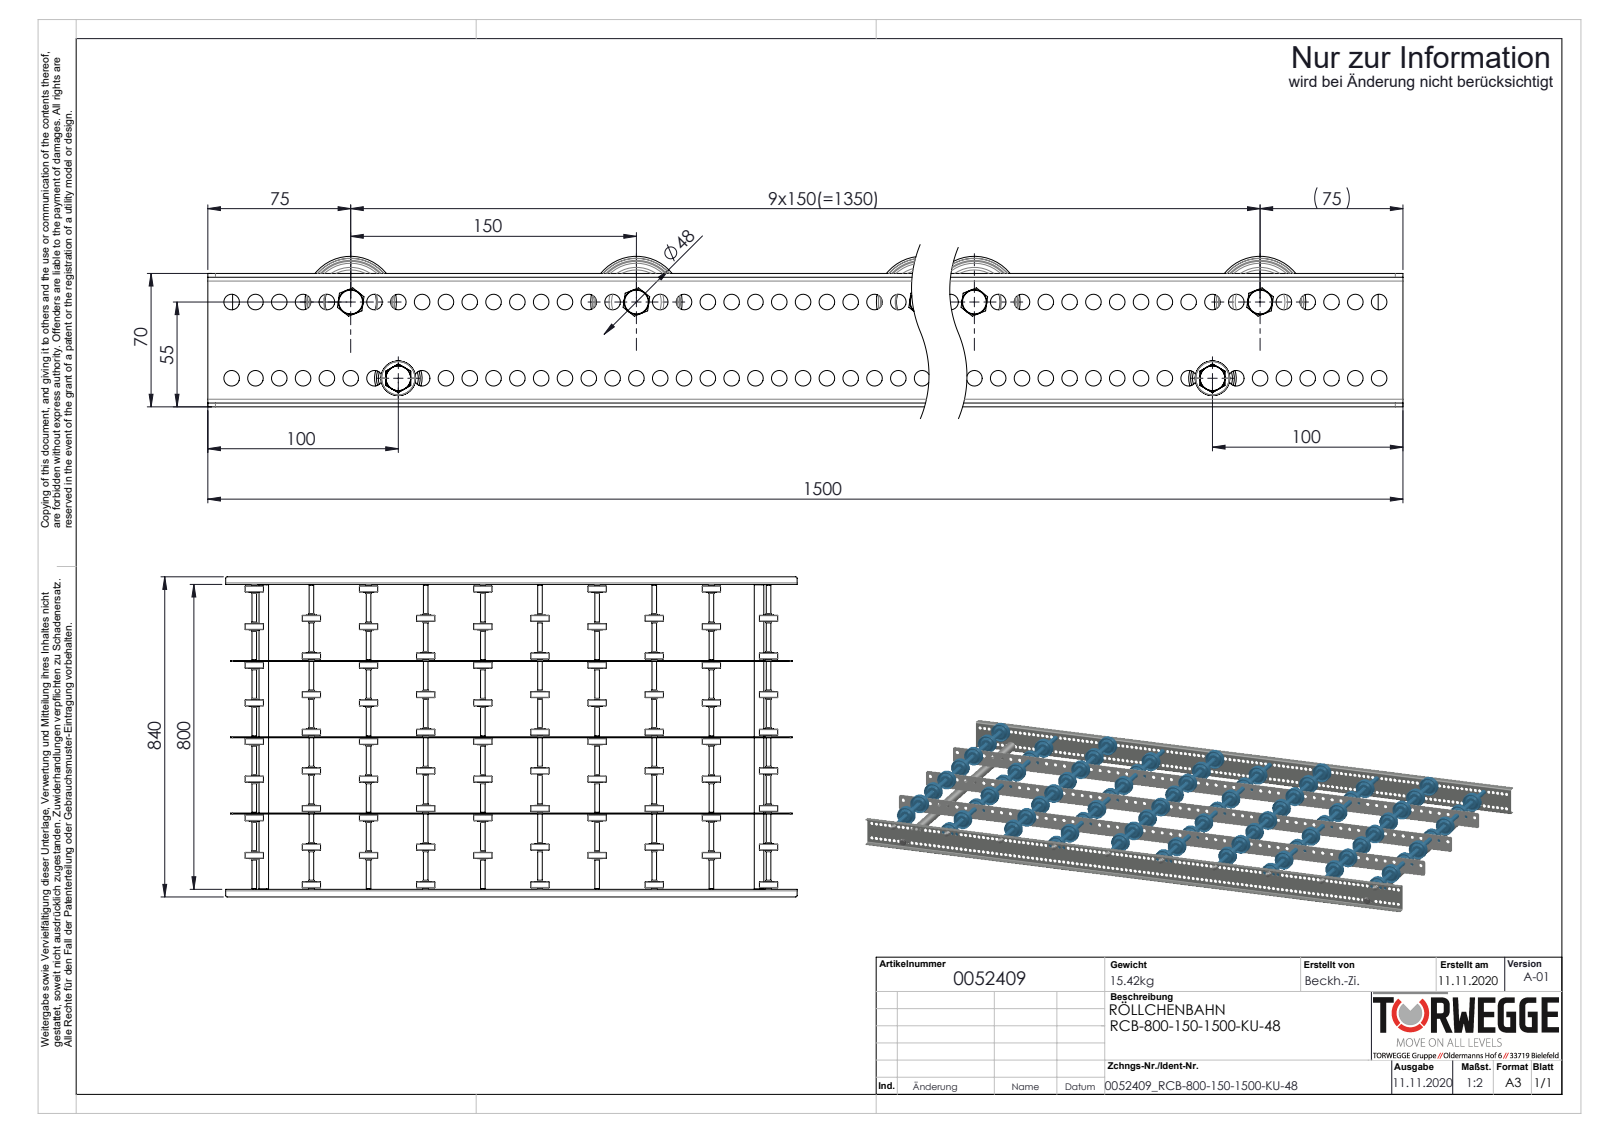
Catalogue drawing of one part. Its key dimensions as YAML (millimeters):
part_name: "0046278_KB-ROHR-12X1,75mm_KFG_L75; Hutmutter_DIN_1587_M8; Röllchenachse-für-Konfiguration_EL800; Traversen_KFG_L800 (+6 more)"
step_written_by: "SolidWorks 2020 (AUTOMOTIVE_DESIGN)"
units: millimeters
bodies: {solids: 205, faces: 8256, planar: 1358, cylindrical: 3234, other: 3664}
overall_size: [1500, 840, 79]
volume: 3458000
surface_area: 2642000
round_holes:
  - {diameter: 8.2, count: 238}
  - {diameter: 8.5, count: 59}
  - {diameter: 6.65, count: 10}
  - {diameter: 9.65, count: 10}
  - {diameter: 13.7, count: 10}
  - {diameter: 6.8, count: 2}
  - {diameter: 21, count: 2}
round_bosses_or_shafts:
  - {diameter: 8, count: 12}
  - {diameter: 48, count: 10}
  - {diameter: 27, count: 10}
  - {diameter: 12.7, count: 10}
  - {diameter: 12.5, count: 10}
  - {diameter: 12, count: 10}
  - {diameter: 25, count: 2}
partial_cylinders:
  - {radius: 4, count: 8}
  - {radius: 2, count: 4}
  - {radius: 5, count: 4}
face_to_face_distances: [200.1, 2, 400.2, 2.5, 197.6, 802, 202.6, 397.7, 68, 804]
hole_center_spacings: [12.5, 25, 37.5, 50, 62.5, 75, 87.5, 100]
